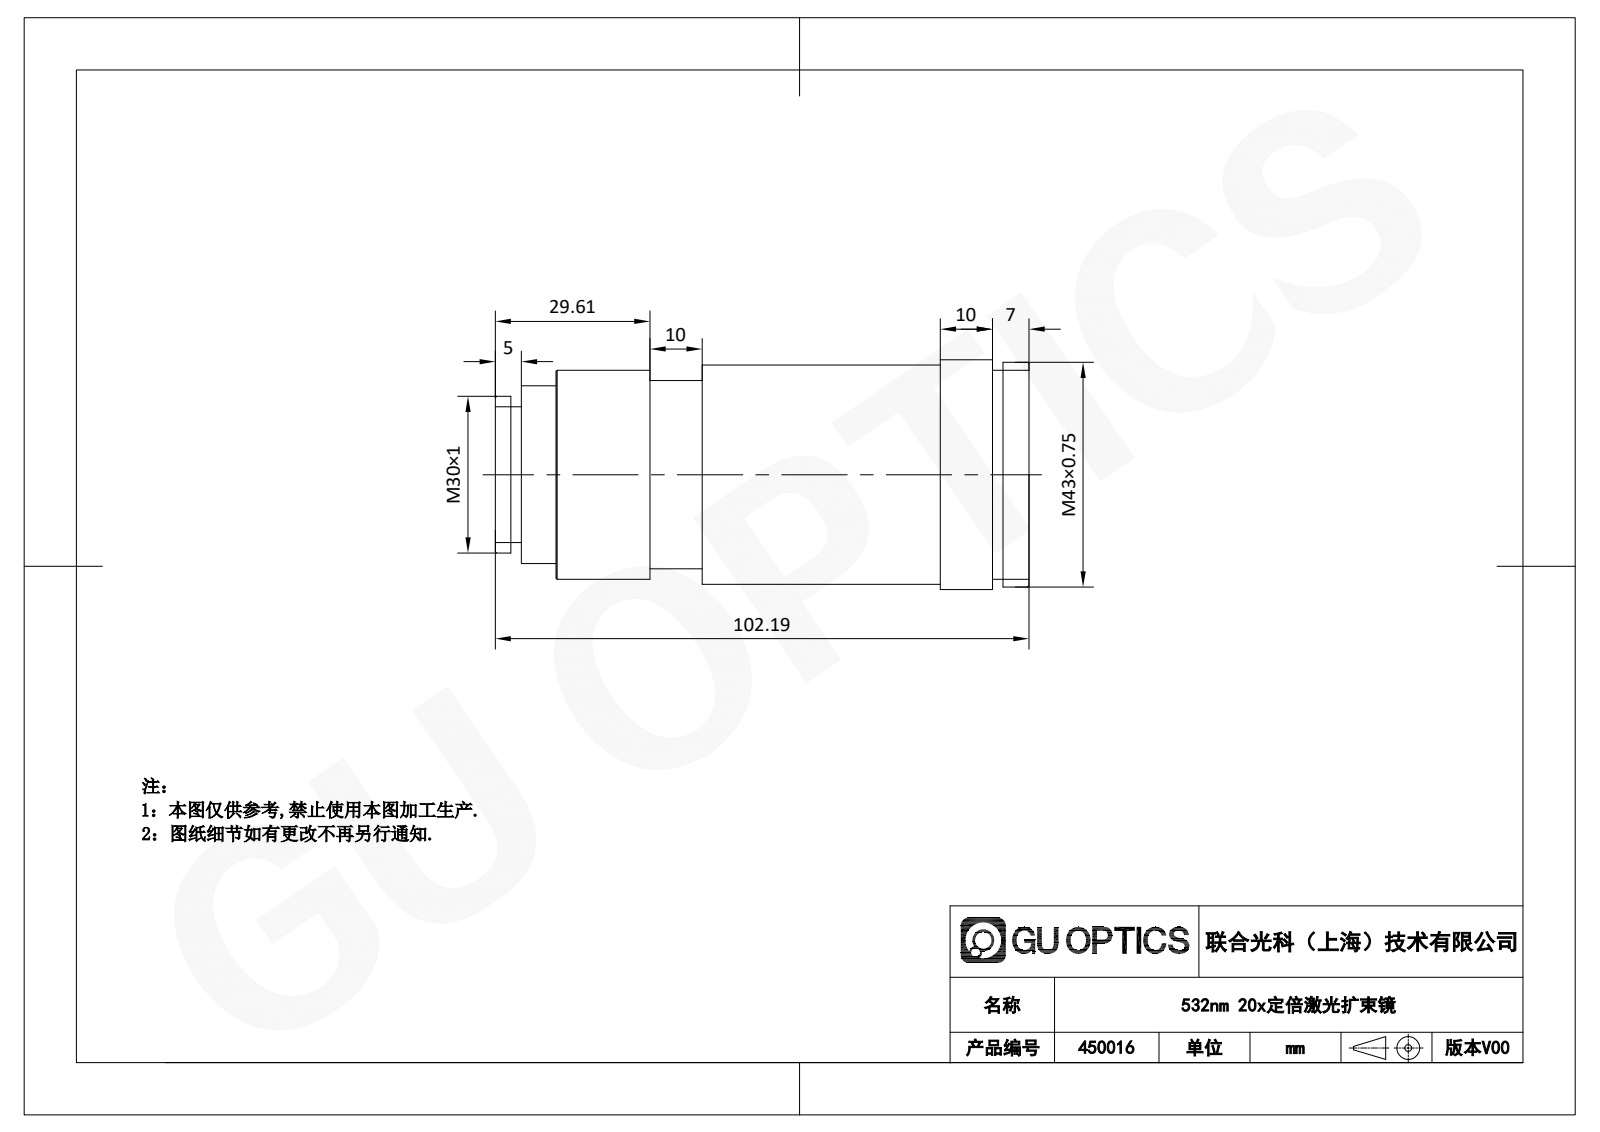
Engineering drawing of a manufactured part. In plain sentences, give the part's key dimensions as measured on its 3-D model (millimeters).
The part is named "450016". Its 3-D file was written by "SolidWorks 2020 (AUTOMOTIVE_DESIGN)". It is 1 solid with 49 faces: 13 planar, 26 cylindrical and 10 other. Overall it measures 102.19 by 44 by 44 millimeters. Its volume is 94 372 cubic millimeters and its surface area 24 309 square millimeters. Round holes: 1 of diameter 8, 1 of diameter 30. Round bosses or shafts: 1 of diameter 44, 1 of diameter 43, 1 of diameter 42, 1 of diameter 40, 1 of diameter 36, 1 of diameter 34, 1 of diameter 26. The main face-to-face distances are 4, 46, 50, 52.19, 98.19, 102.19, 5, 97.19, 3, 95.19.
